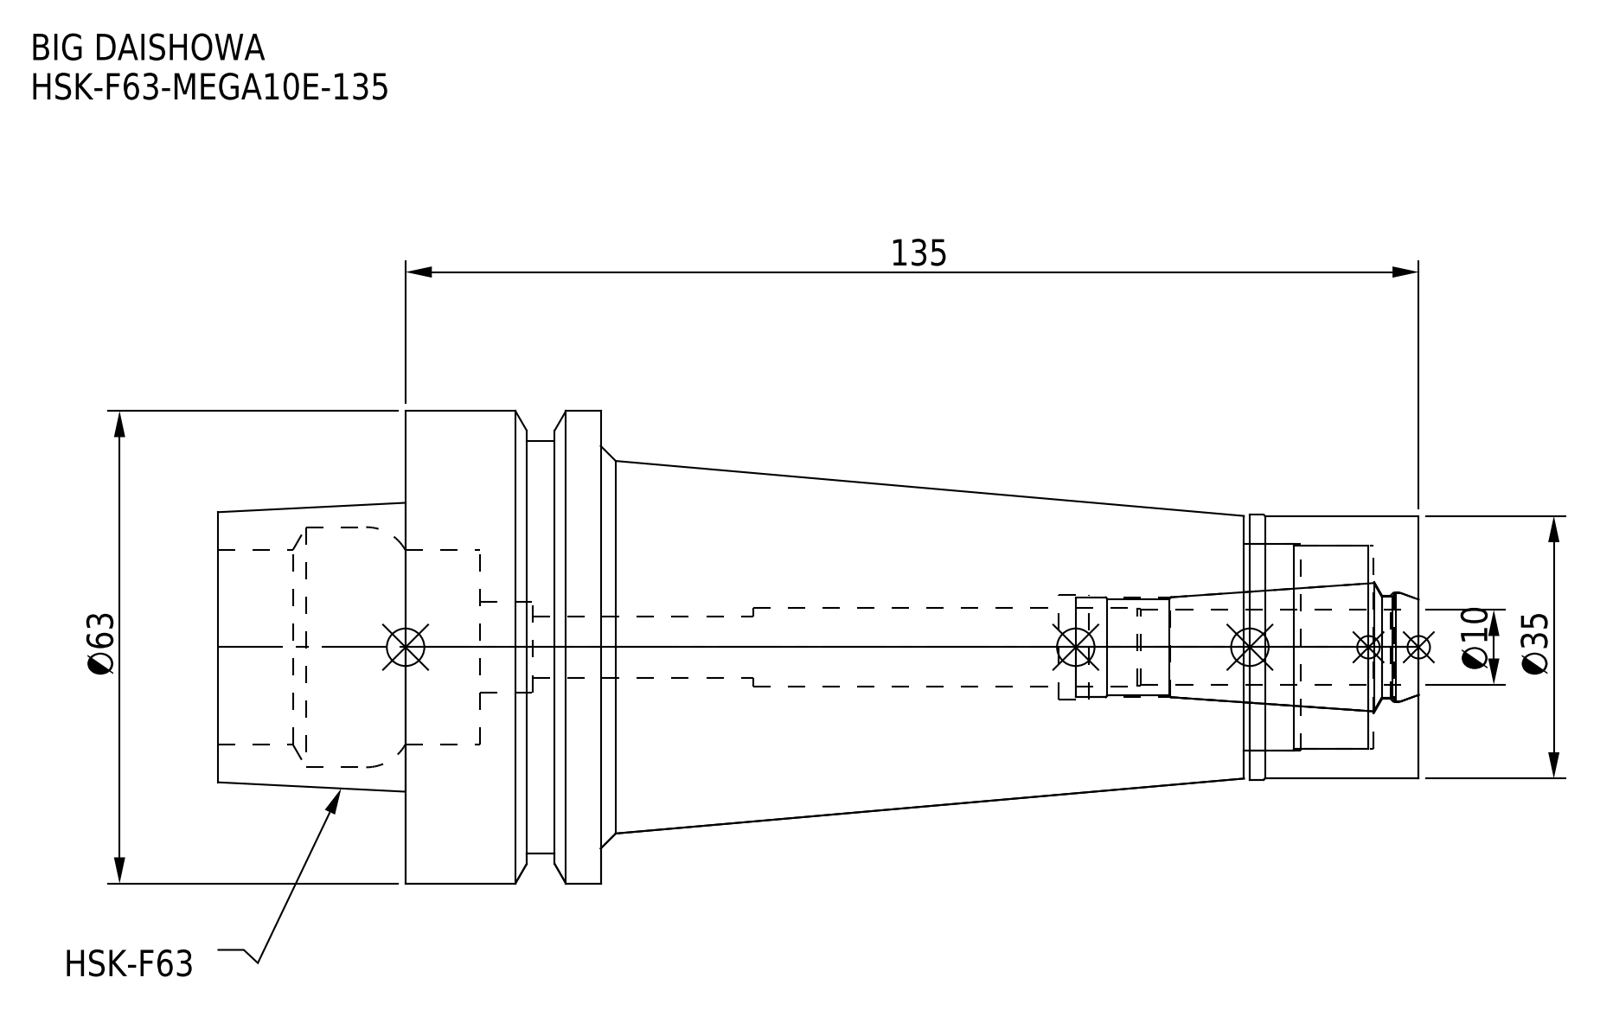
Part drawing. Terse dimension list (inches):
name: HSK-F63-MEGA10E-135_1.stp; HSK-F63-MEGA10E-135; DXF_TEMP_ASSY_ASM_4_ASM.stp; HSK-F63-MEGA10E-135-100.stp (+3 more)
written by: SolidWorks 2019 (CONFIG_CONTROL_DESIGN)
unit: in
bodies: 2 solids, 81 faces (17 planar, 40 cylindrical, 24 other)
size: 6.299 × 2.48 × 2.48
volume: 13.06 in³; area: 62.13 in²
holes: 1× ⌀0.325, 1× ⌀0.409, 1× ⌀0.472, 1× ⌀0.524, 1× ⌀0.543, 1× ⌀0.547, 1× ⌀0.579, 1× ⌀1.024, 1× ⌀1.063, 1× ⌀1.083, 1× ⌀1.26
bosses: 1× ⌀2.48, 1× ⌀2.165, 1× ⌀1.39, 1× ⌀1.378
face distances: 1.024, 4.291, 5.315, 6.299, 2.008, 0.984, 4.923, 0.632, 0.392, 1.376
